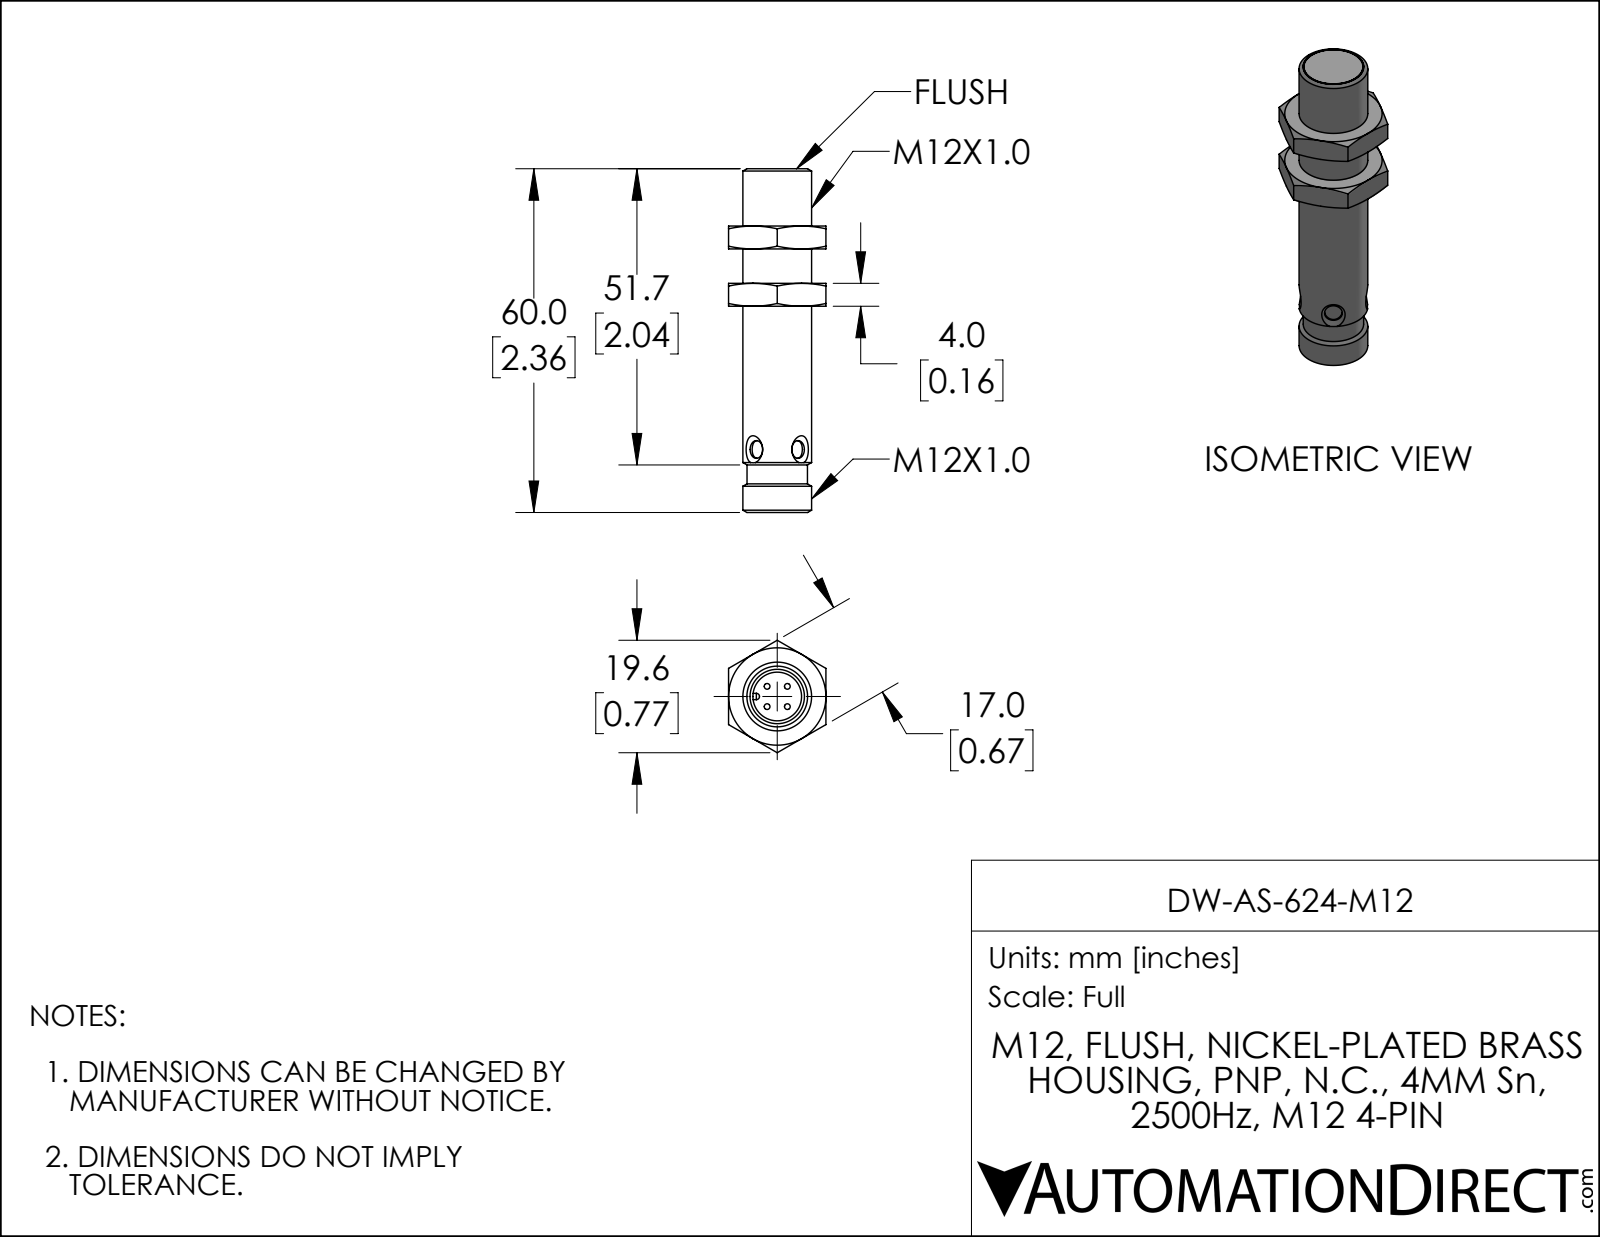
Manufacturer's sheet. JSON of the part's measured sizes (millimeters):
{"part_name": "DW-AS-624-M12", "step_written_by": "SolidWorks 2019 (AUTOMOTIVE_DESIGN)", "units": "millimeters", "bodies": {"solids": 1, "faces": 83, "planar": 23, "cylindrical": 22, "other": 38}, "overall_size": [60, 19.6, 17], "volume_mm3": 7260, "surface_area_mm2": 3519, "round_holes": [[3.1, 2], [8.5, 1], [10.5, 1]], "round_bosses_or_shafts": [[1, 4], [12, 1], [10.5, 1], [10.3, 1]], "partial_cylinders_radius": [[0.6, 2], [4.9, 1]], "face_to_face_distances": [10, 4, 17, 14, 6, 20, 24, 51.3, 41.3, 37.3]}
